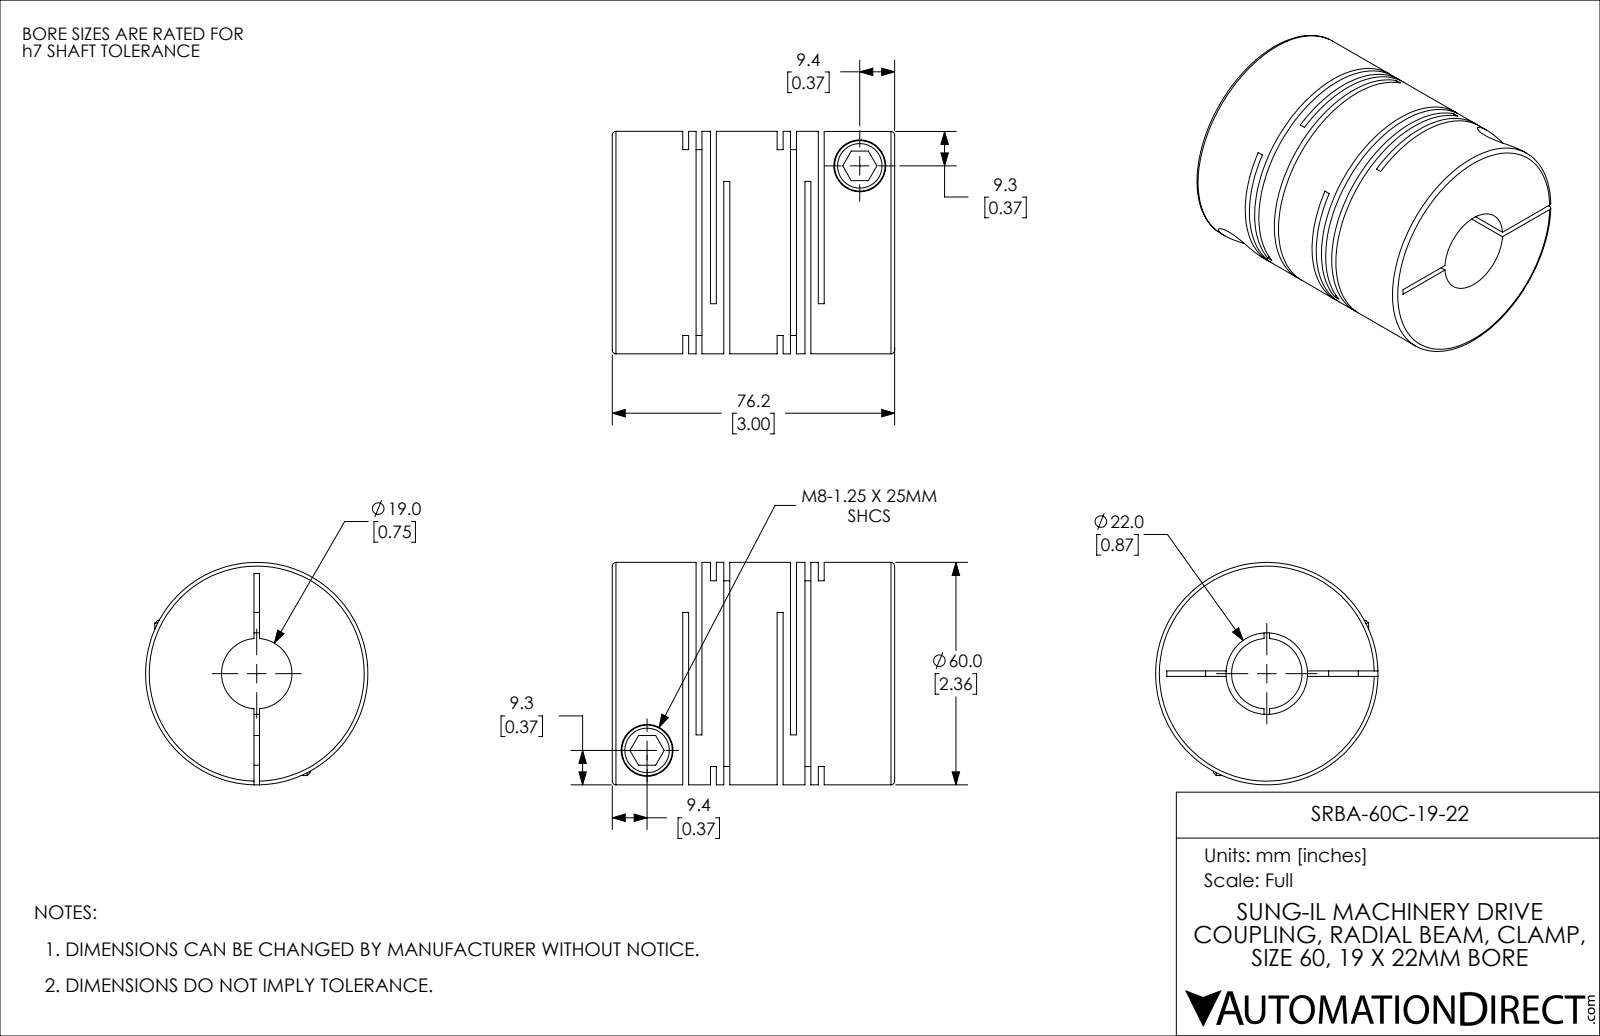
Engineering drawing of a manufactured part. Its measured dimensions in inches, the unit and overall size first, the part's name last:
Units: inches
Overall size (bounding box): 3 × 2.362 × 2.362
Round holes (diameter × count): ⌀0.315 ×2, ⌀0.551 ×2, ⌀0.748 ×1, ⌀0.866 ×1
Round bosses / shafts (diameter × count): ⌀0.535 ×2, ⌀2.362 ×1
Main face-to-face distances: 0.063, 0.142, 0.295, 1.004, 1.299, 1.067, 0.709, 0.079, 0.232, 0.941
Volume: 9.64 in³ · Surface area: 90.38 in²
Bodies: 1 solid, 115 faces (60 planar, 42 cylindrical, 13 other)
Part name (STEP PRODUCT): SRBA-60C-19-22
STEP written by: SolidWorks 2021 (CONFIG_CONTROL_DESIGN)
